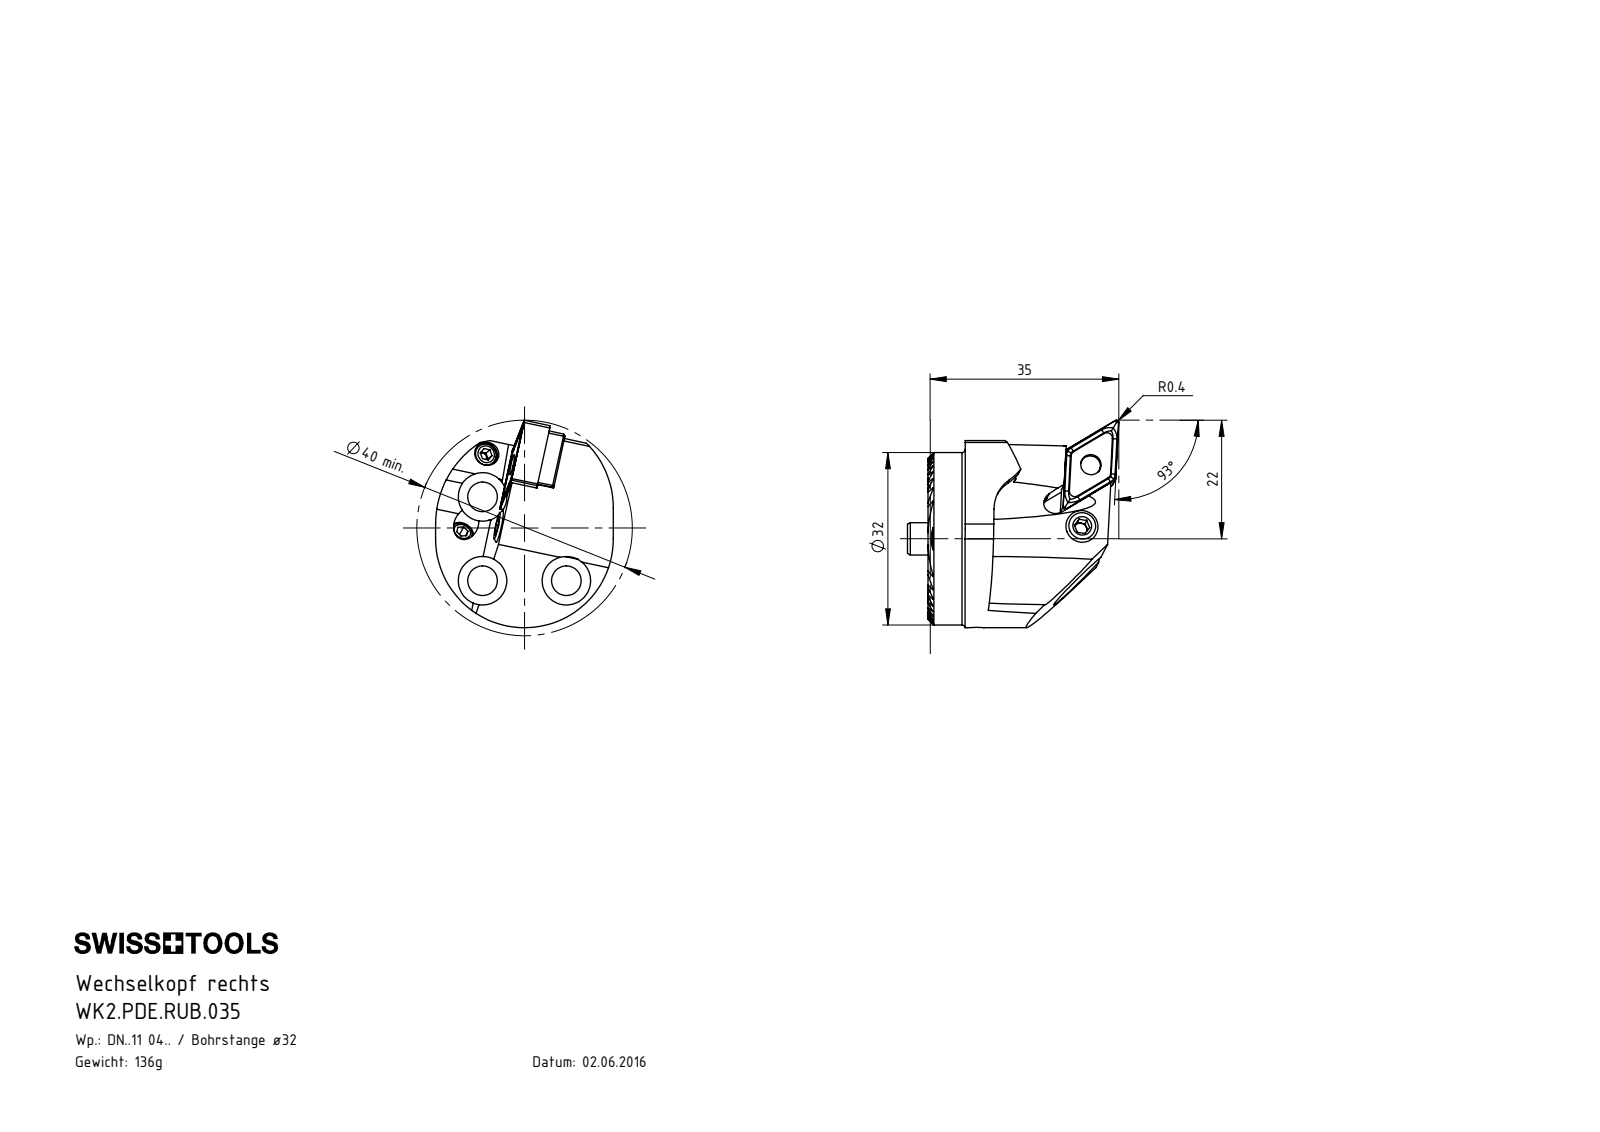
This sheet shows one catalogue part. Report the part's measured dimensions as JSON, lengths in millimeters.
{"part_name": "WDE-ER4.101.017_A; WKX-ER1.004.005_A_PreviewCfg; WK2-ER1.001.012_A_Fertigbearbeitung; WK2-PDE.RUB.035_A (+6 more)", "step_written_by": "SolidWorks 2017 (AUTOMOTIVE_DESIGN)", "units": "millimeters", "bodies": {"solids": 15, "faces": 480, "planar": 257, "cylindrical": 112, "other": 111}, "overall_size": [39.21, 38.5, 33], "volume_mm3": 17724, "surface_area_mm2": 10211, "round_holes": [[2.38, 3], [2.5, 3], [5.5, 3], [9, 3], [1.7, 2], [3, 2], [3.3, 2], [4.5, 2], [3.81, 1], [4.2, 1], [4.8, 1], [5, 1]], "round_bosses_or_shafts": [[3, 3], [6, 2], [4, 2], [32, 1], [12, 1], [5.9, 1], [2.87, 1]], "partial_cylinders_radius": [[0.12, 22], [0.4, 8], [2.1, 5], [7, 2], [1.83, 1], [1.85, 1], [2.25, 1], [2.35, 1]], "face_to_face_distances": [1.3, 2.6, 3.9, 5.2, 6.5, 7.8, 12.99, 11.69, 14.29, 10.39], "hole_center_spacings": [11, 11.8, 15.56, 22.01]}
